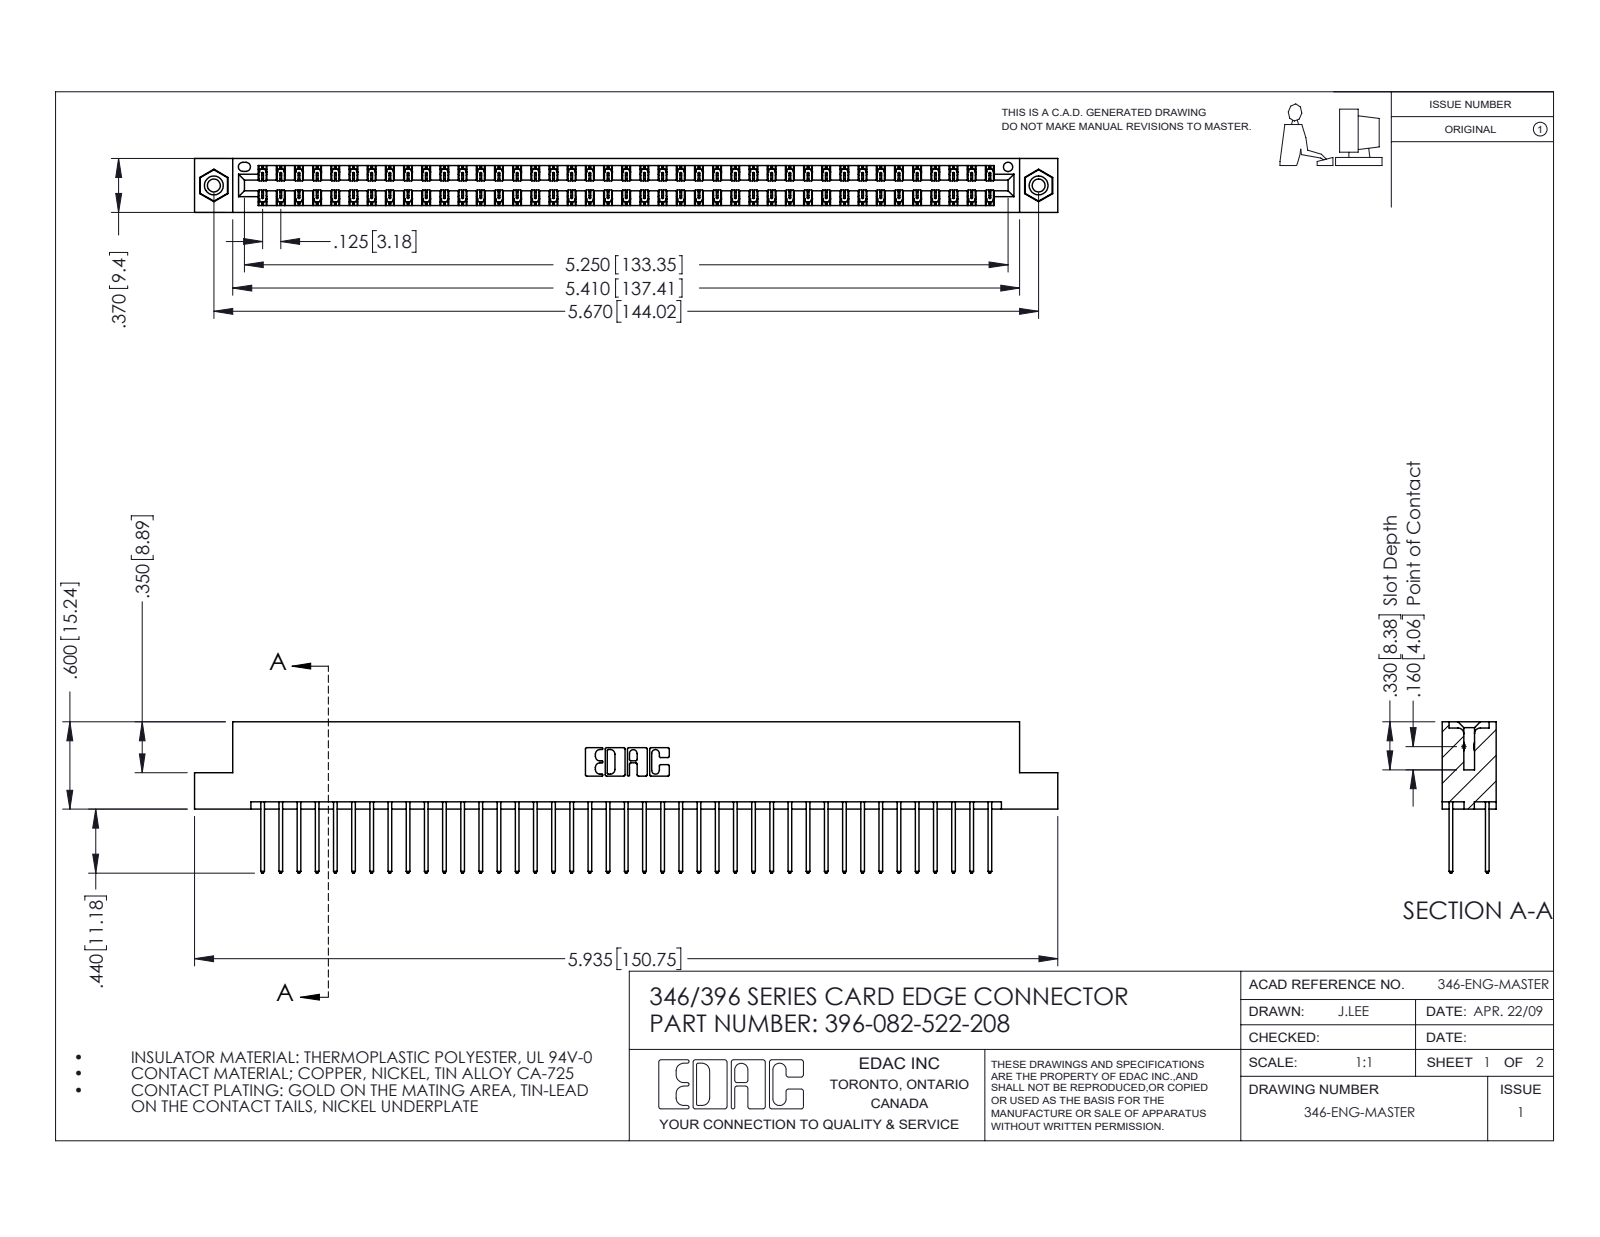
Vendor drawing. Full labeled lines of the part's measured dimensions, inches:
Part name (STEP PRODUCT): 345-292-001_345-293-122; 345-250-001_345-250-003-102; 396-082-522-208; 346 Part_Flush Mounting Lugs - 0.156 Dia-TI
STEP written by: SolidWorks 2016 (CONFIG_CONTROL_DESIGN)
Units: inches
Bodies: 85 solids, 4446 faces (2978 planar, 1452 cylindrical, 16 other)
Overall size (bounding box): 5.935 × 1.04 × 0.37
Volume: 0.909 in³ · Surface area: 33.25 in²
Round holes (diameter × count): ⌀0.089 ×2, ⌀0.125 ×2, ⌀0.156 ×2, ⌀0.064 ×1
Round bosses / shafts (diameter × count): ⌀0.155 ×2
Partial cylindrical surfaces — rounded edges, fillets, slot ends (radius × count): R0.006 ×123, R0.01 ×82, R0.01 ×22, R0.007 ×6, R0.031 ×6, R0.026 ×3, R0.014 ×2, R0.022 ×2
Main face-to-face distances: 0.048, 0.322, 0.25, 0.37, 0.072, 0.298, 0.025, 0.275, 0.148, 0.222
Hole centre spacings: 0.246, 5.461, 5.67
